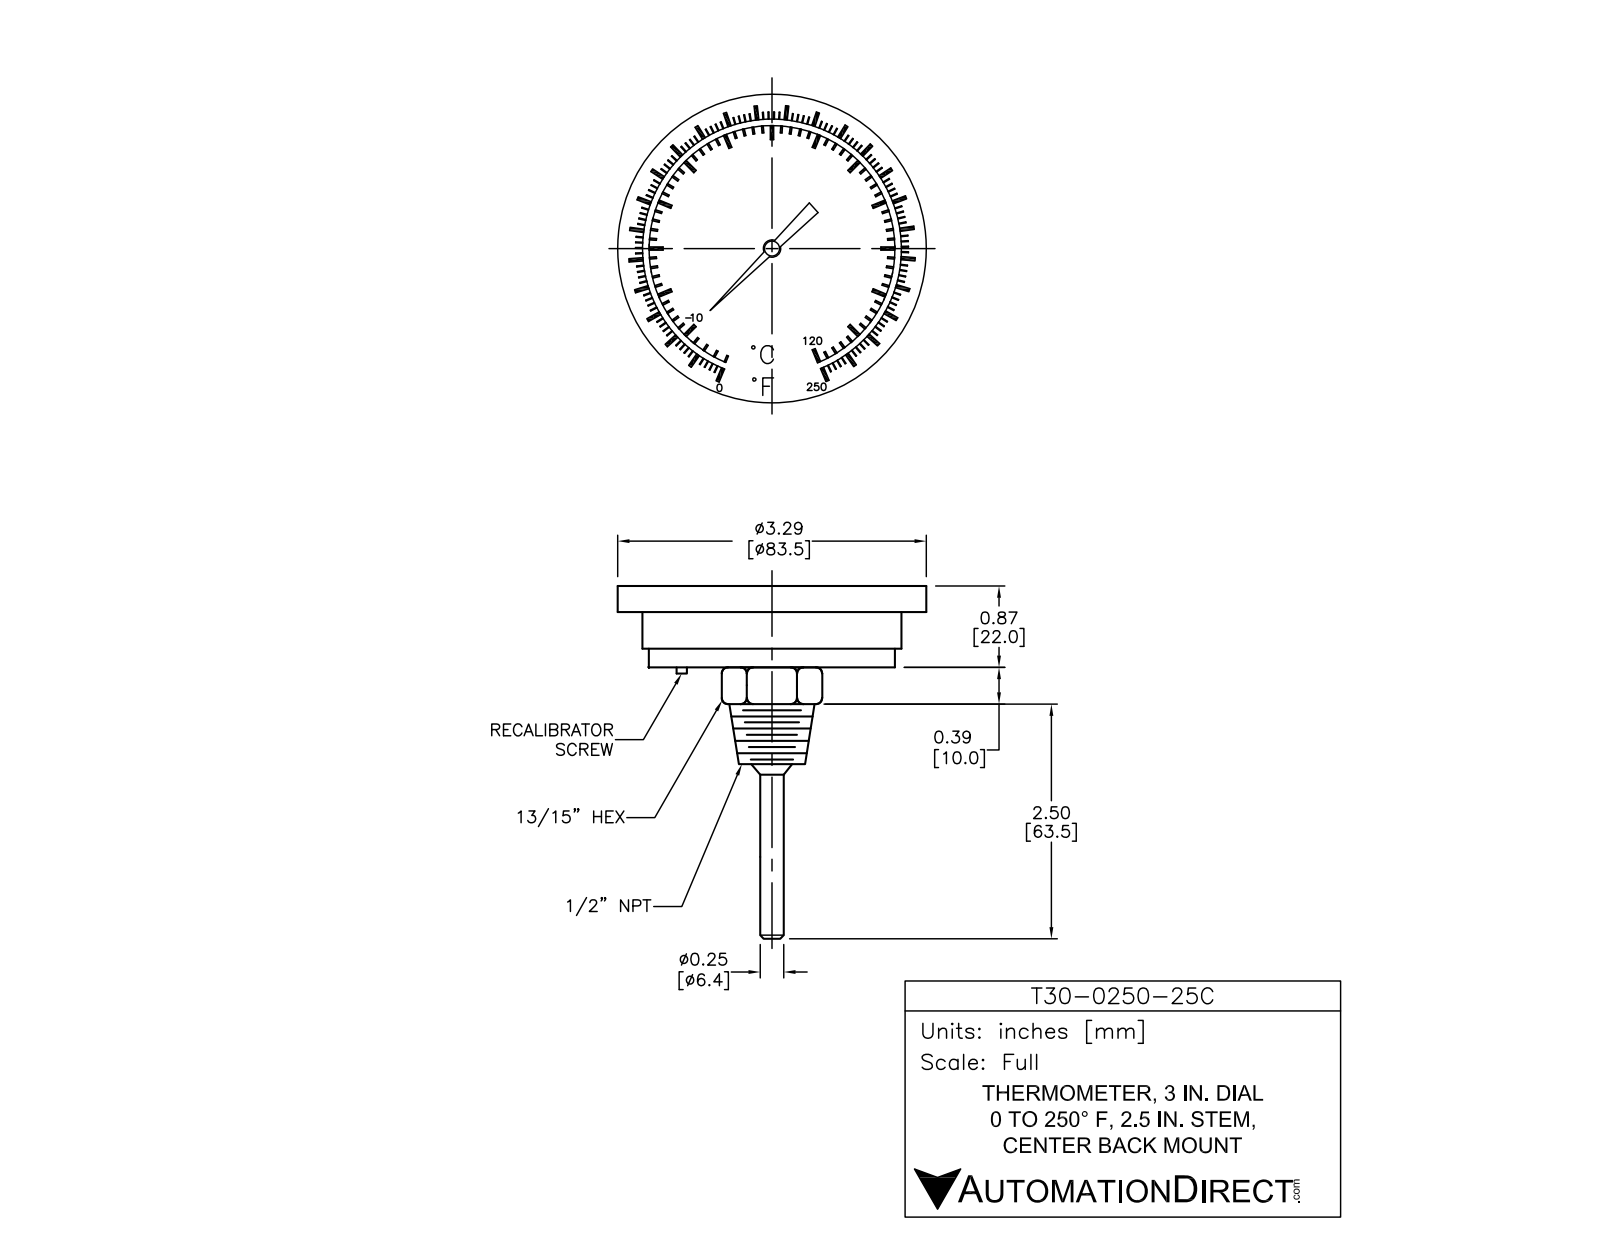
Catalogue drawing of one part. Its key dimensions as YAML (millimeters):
part_name: "T30-0250-25C"
step_written_by: "SolidWorks 2021 (AUTOMOTIVE_DESIGN)"
units: millimeters
bodies: {solids: 73, faces: 1252, planar: 1096, cylindrical: 85, other: 71}
overall_size: [95.5, 83.6, 83.6]
volume: 50360
surface_area: 21310
round_holes:
  - {diameter: 1.7, count: 1}
  - {diameter: 68.3, count: 1}
round_bosses_or_shafts:
  - {diameter: 83.6, count: 1}
  - {diameter: 70.1, count: 1}
  - {diameter: 66.5, count: 1}
  - {diameter: 21.5, count: 1}
  - {diameter: 6.6, count: 1}
partial_cylinders:
  - {radius: 1, count: 1}
  - {radius: 18, count: 1}
  - {radius: 21.8, count: 1}
  - {radius: 24.6, count: 1}
  - {radius: 28.4, count: 1}
face_to_face_distances: [5.6, 2, 7.6, 22.1, 16.5, 14.5, 15, 9.3, 7.4, 7.1]
